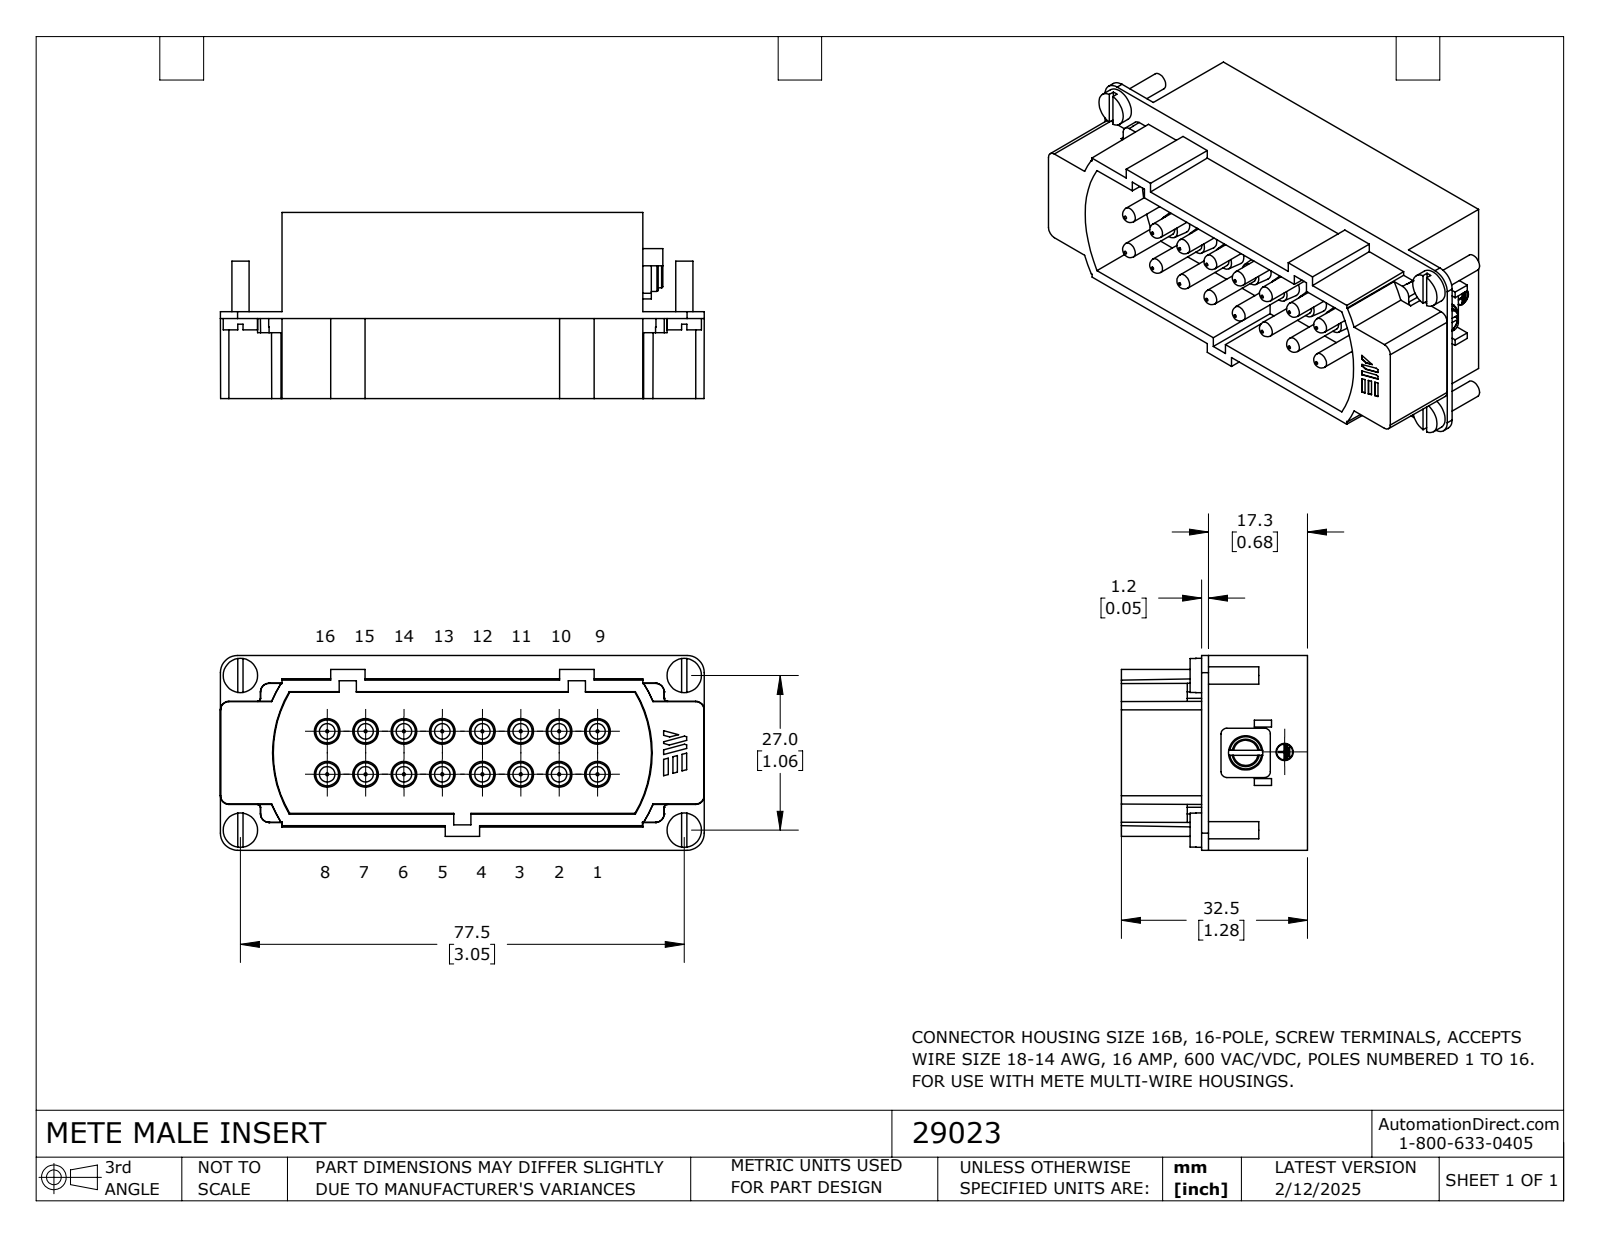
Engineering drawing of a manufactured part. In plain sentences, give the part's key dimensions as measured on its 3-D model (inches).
The part is named "29023". Its 3-D file was written by "SolidWorks 2024 (CONFIG_CONTROL_DESIGN)". It is 1 solid with 400 faces: 214 planar, 97 cylindrical and 89 other. Overall it measures 3.327 by 1.339 by 1.28 inches. Its volume is 3.043 cubic inches and its surface area 30.18 square inches. Round holes: 16 of diameter 0.177, 1 of diameter 0.118. Round bosses or shafts: 16 of diameter 0.106, 5 of diameter 0.236, 4 of diameter 0.118, 1 of diameter 0.189, 1 of diameter 0.11. Partial cylindrical surfaces (rounded edges, fillets, slot ends): 4 of radius 0.039, 4 of radius 0.118. The main face-to-face distances are 0.728, 1.339, 0.047, 0.681, 0.551, 0.598, 1.28, 2.48, 0.394, 0.335. The hole center spacings are 0.264, 0.396, 0.528, 0.605, 0.791, 0.844, 0.295, 1.055.
